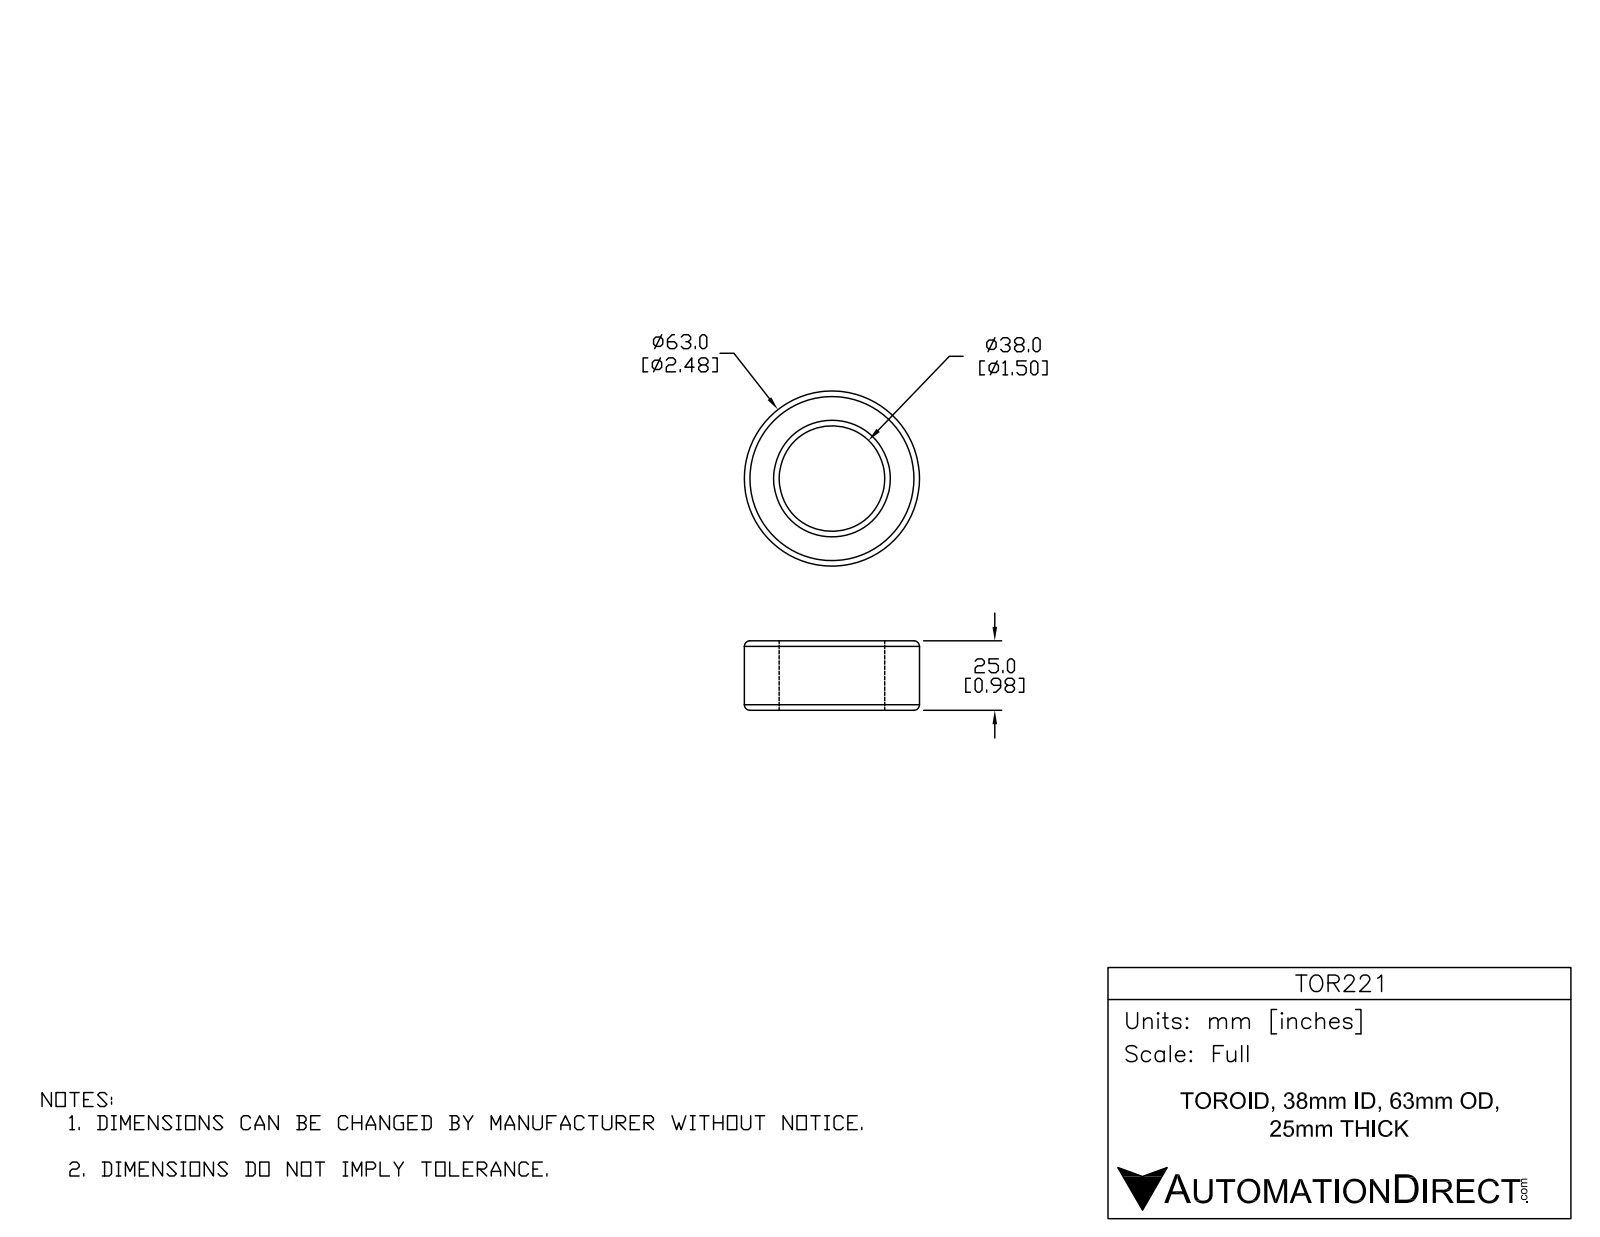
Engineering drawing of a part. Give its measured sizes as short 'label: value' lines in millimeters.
name: TOR221
written by: SolidWorks 2015 (AUTOMOTIVE_DESIGN)
unit: mm
bodies: 1 solid, 14 faces (2 planar, 4 cylindrical, 8 other)
size: 63 × 63 × 25
volume: 49 034 mm³; area: 11 354 mm²
holes: 1× ⌀38
bosses: 1× ⌀63
face distances: 25
